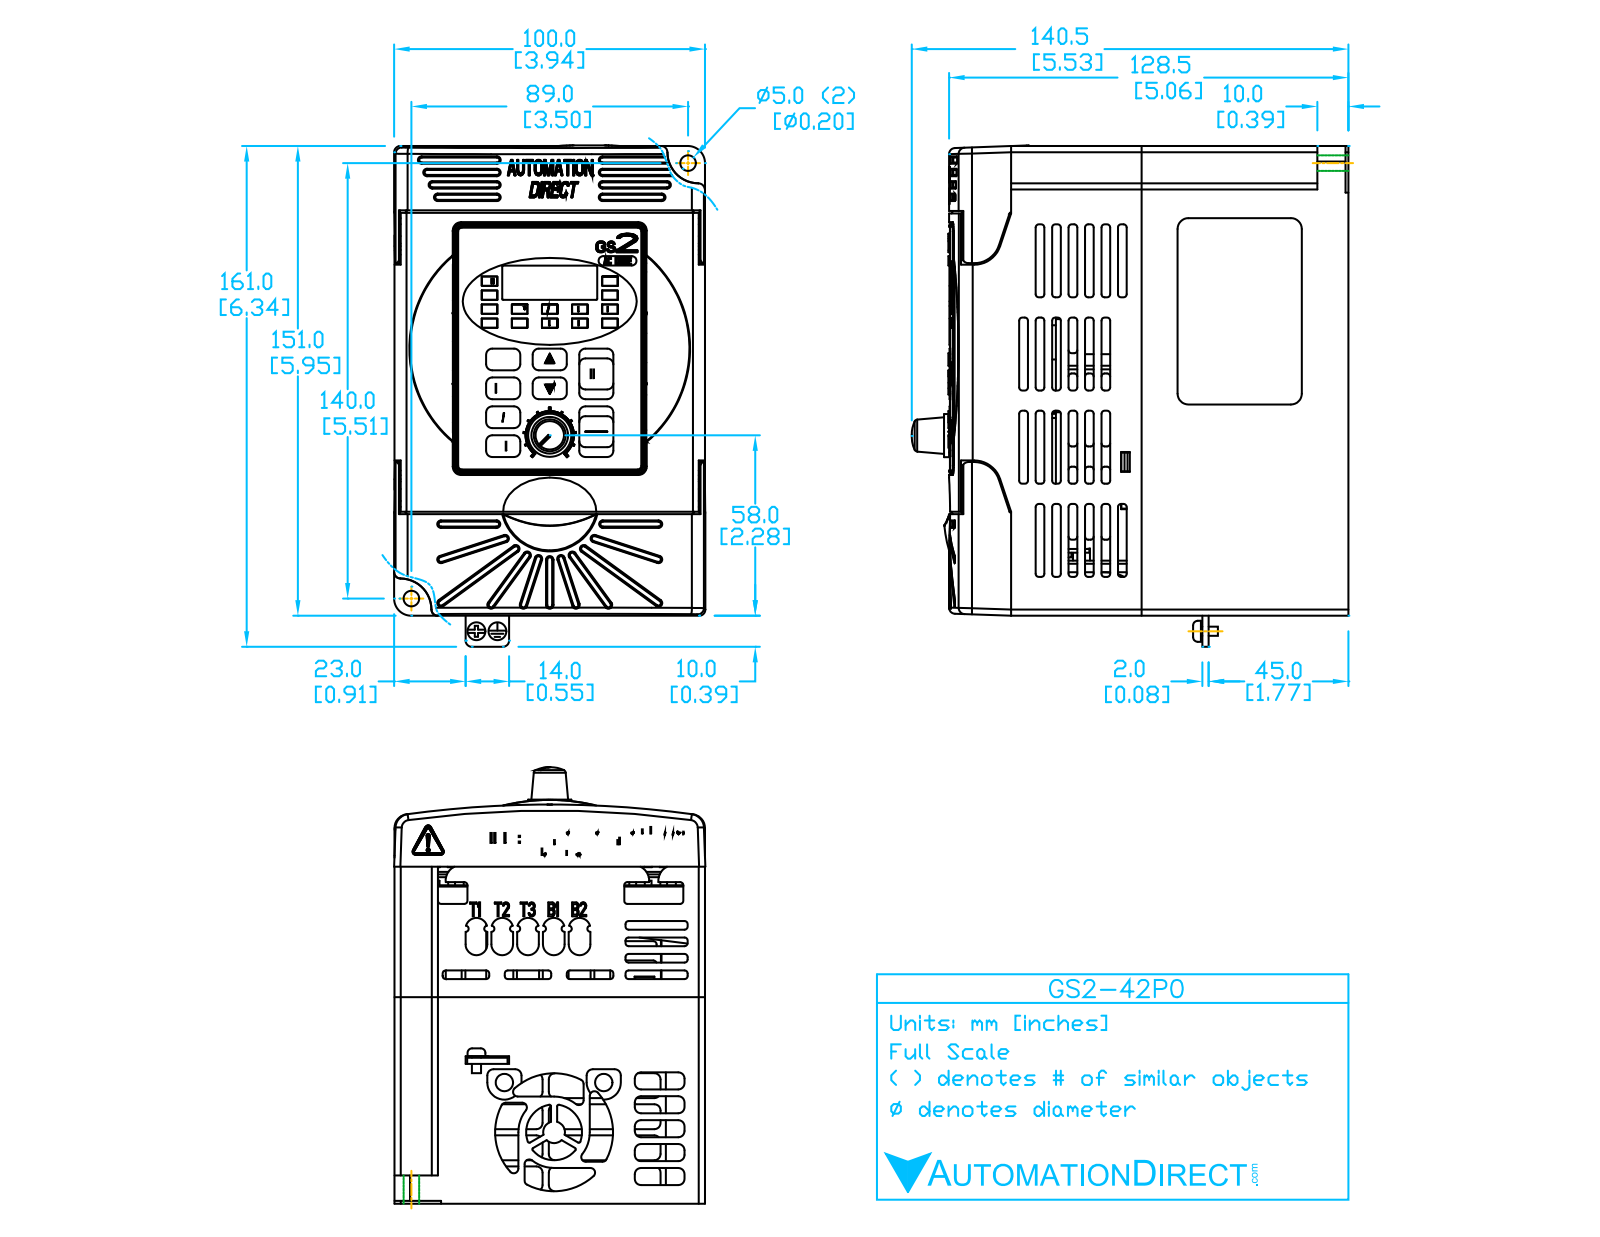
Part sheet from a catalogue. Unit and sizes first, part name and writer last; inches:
Units: inches
Overall size (bounding box): 6.345 × 5.495 × 3.94
Round holes (diameter × count): ⌀0.2 ×2, ⌀0.7 ×1, ⌀1.46 ×1
Round bosses / shafts (diameter × count): ⌀0.545 ×1, ⌀0.22 ×1, ⌀0.15 ×1
Partial cylindrical surfaces — rounded edges, fillets, slot ends (radius × count): R0.04 ×40, R0.06 ×24, R0.125 ×10, R0.02 ×8, R0.03 ×8, R0.045 ×6, R0.2 ×6, R0.1 ×4
Main face-to-face distances: 3.94, 5.95, 4.256, 4.266, 0.015, 5.935, 0.03, 0.761, 3.179, 0.03
Hole centre spacings: 6.528
Volume: 112.9 in³ · Surface area: 196.7 in²
Bodies: 1 solid, 744 faces (317 planar, 228 cylindrical, 199 other)
Part name (STEP PRODUCT): GS2-42P0
STEP written by: SolidWorks 2013 (AUTOMOTIVE_DESIGN)
